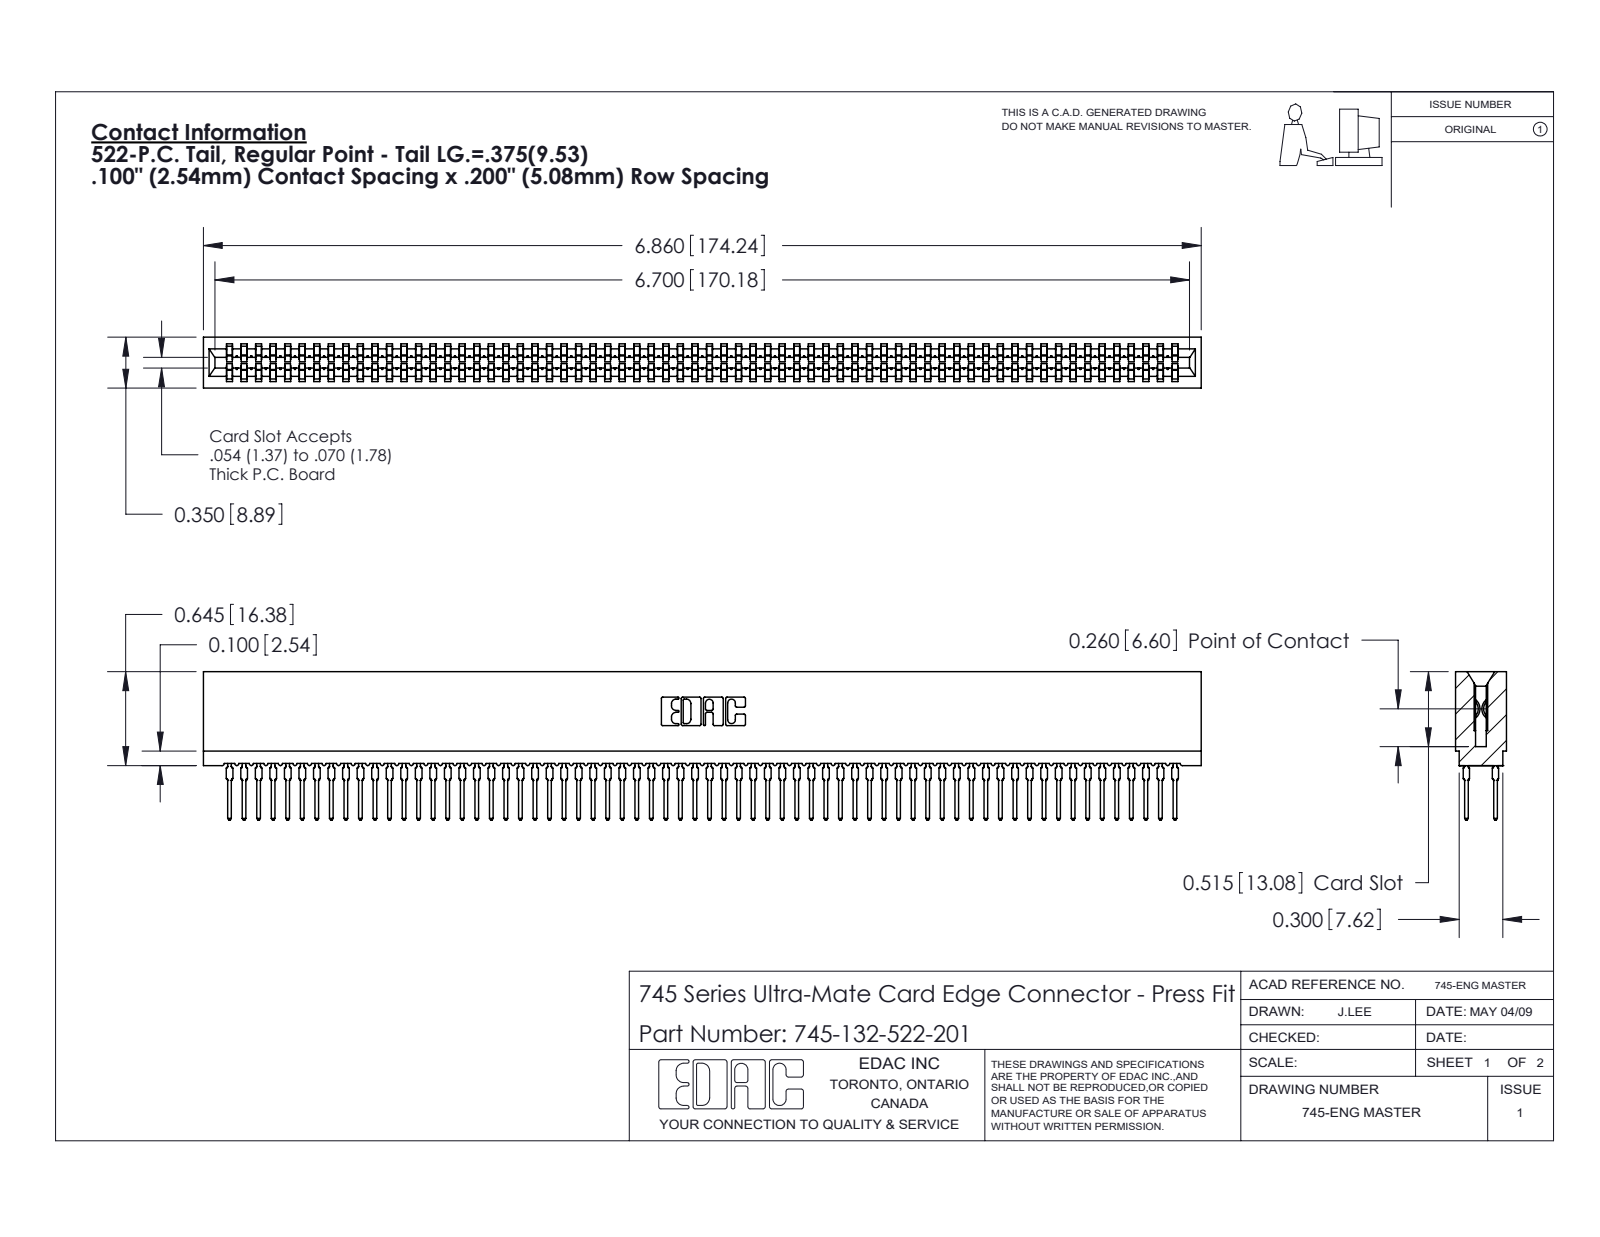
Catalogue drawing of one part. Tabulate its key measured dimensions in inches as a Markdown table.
| quantity | value |
| --- | --- |
| part name | 745-132-522-201; 745-292-001_522; 745 Part_Insulator Option - 01 |
| STEP written by | SolidWorks 2020 (CONFIG_CONTROL_DESIGN) |
| units | inches |
| bodies | 133 solids, 11909 faces (6127 planar, 2350 cylindrical, 3432 other) |
| overall size | 6.86 × 1.021 × 0.35 |
| volume | 0.957 in³ |
| surface area | 51 in² |
| partial cylindrical surfaces (radius × count) | 0.021 × 264, 0.015 × 132, 0.01 × 22, 0.005 × 8, 0.011 × 8, 0.007 × 6, 0.031 × 6, 0.026 × 3 |
| main face-to-face distances | 0.35, 0.063, 0.287, 0.045, 0.305, 0.018, 0.243, 0.138, 0.212, 0.093 |
